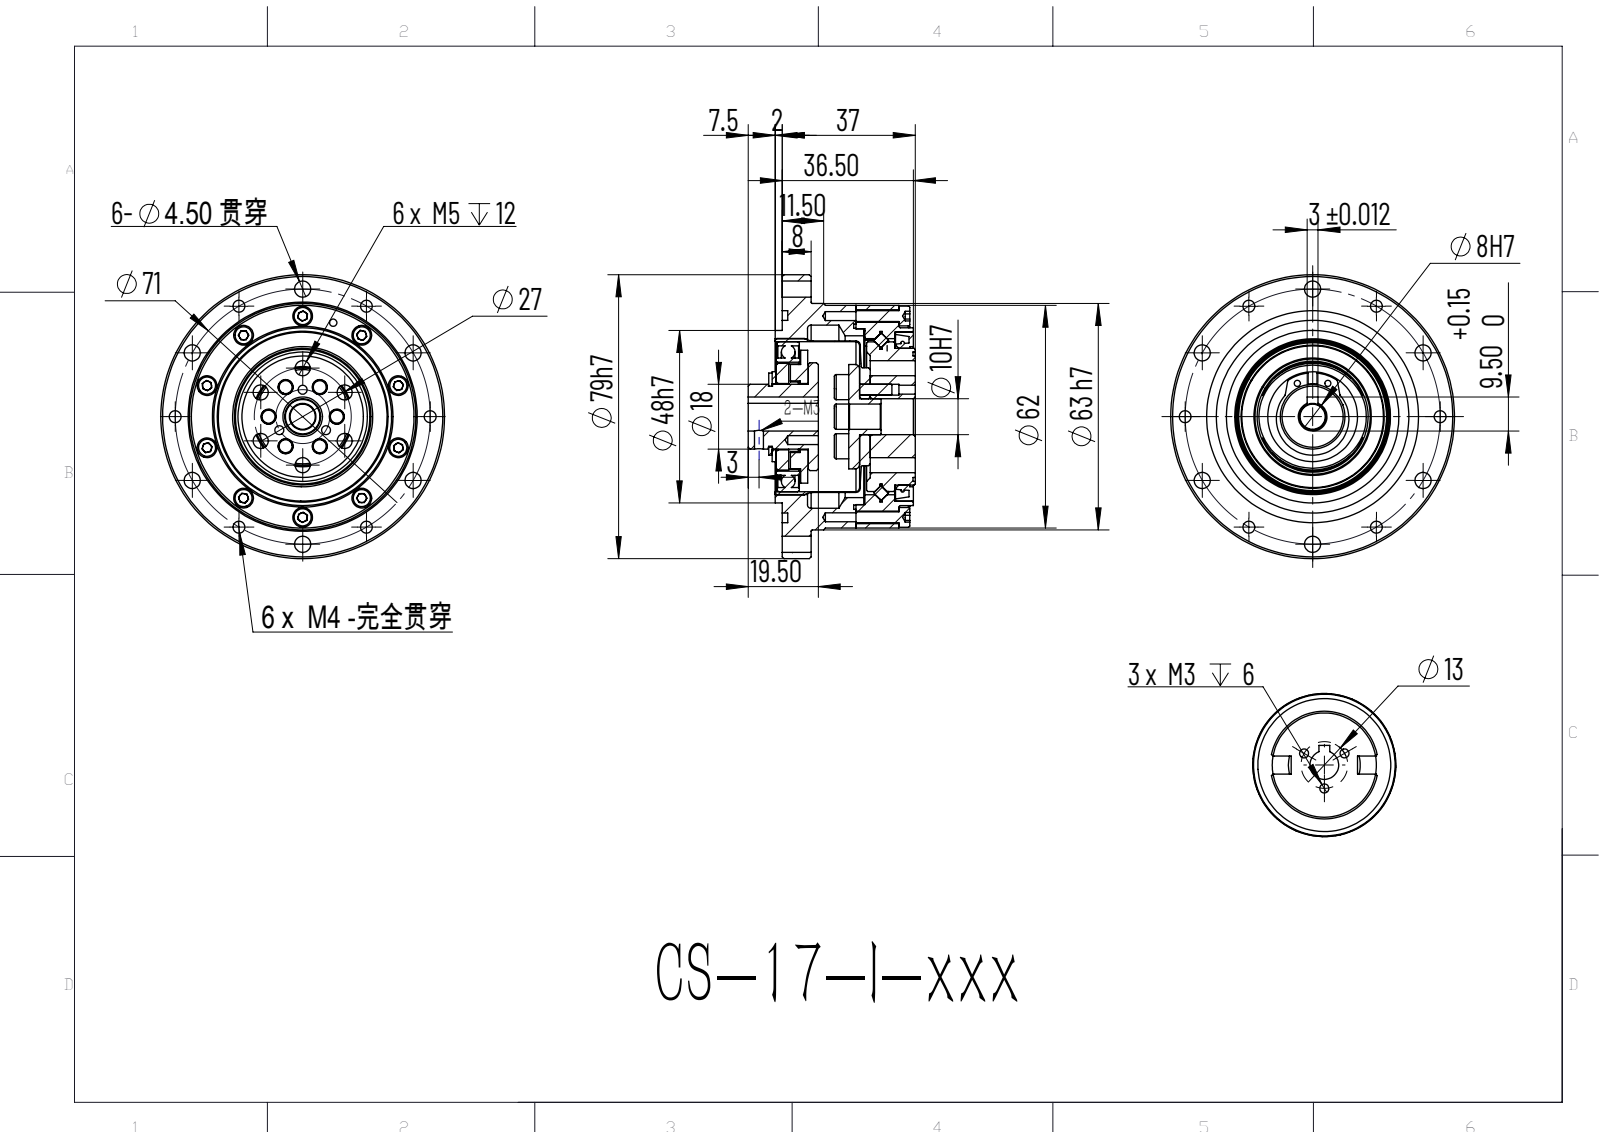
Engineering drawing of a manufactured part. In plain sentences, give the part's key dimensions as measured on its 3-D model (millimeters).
The part is named "CS-17-I; 17-50??; hexagon socket head cap screws gb_GB_FASTENER_SCREWS_HSHCS M4X10-N; hexagon socket head cap screws gb_GB_FASTENER_SCREWS_HSHCS M3X12-C (+8 more)". Its 3-D file was written by "ONSHAPE BY PTC INC, 1.201 (AP242_MANAGED_MODEL_BASED_3D_ENGINEERING_MIM_LF)". It is 76 solids with 2017 faces: 648 planar, 822 cylindrical and 547 other. Overall it measures 79 by 79 by 46.48 millimeters. Its volume is 91 184 cubic millimeters and its surface area 68 269 square millimeters. Round holes: 17 of diameter 2.5, 12 of diameter 4.2, 10 of diameter 3.5, 6 of diameter 3.3, 6 of diameter 4.5, 6 of diameter 5.5, 3 of diameter 3, 3 of diameter 3.2, 2 of diameter 1.7, 1 of diameter 7, 1 of diameter 8, 1 of diameter 10. Round bosses or shafts: 54 of diameter 3, 10 of diameter 5.5, 6 of diameter 7, 6 of diameter 4, 1 of diameter 79, 1 of diameter 63, 1 of diameter 62, 1 of diameter 53.6. Partial cylindrical surfaces (rounded edges, fillets, slot ends): 200 of radius 0.26, 200 of radius 0.3, 2 of radius 0.2, 2 of radius 0.5, 1 of radius 10, 1 of radius 10.1, 1 of radius 12.2, 1 of radius 21.22. The main face-to-face distances are 8, 20.5, 13.5, 12.5, 24.5, 1, 12, 21.5, 3, 4. The hole center spacings are 35.5, 9.5, 27.68, 31.83, 41.08, 50.2, 68.58, 28.
